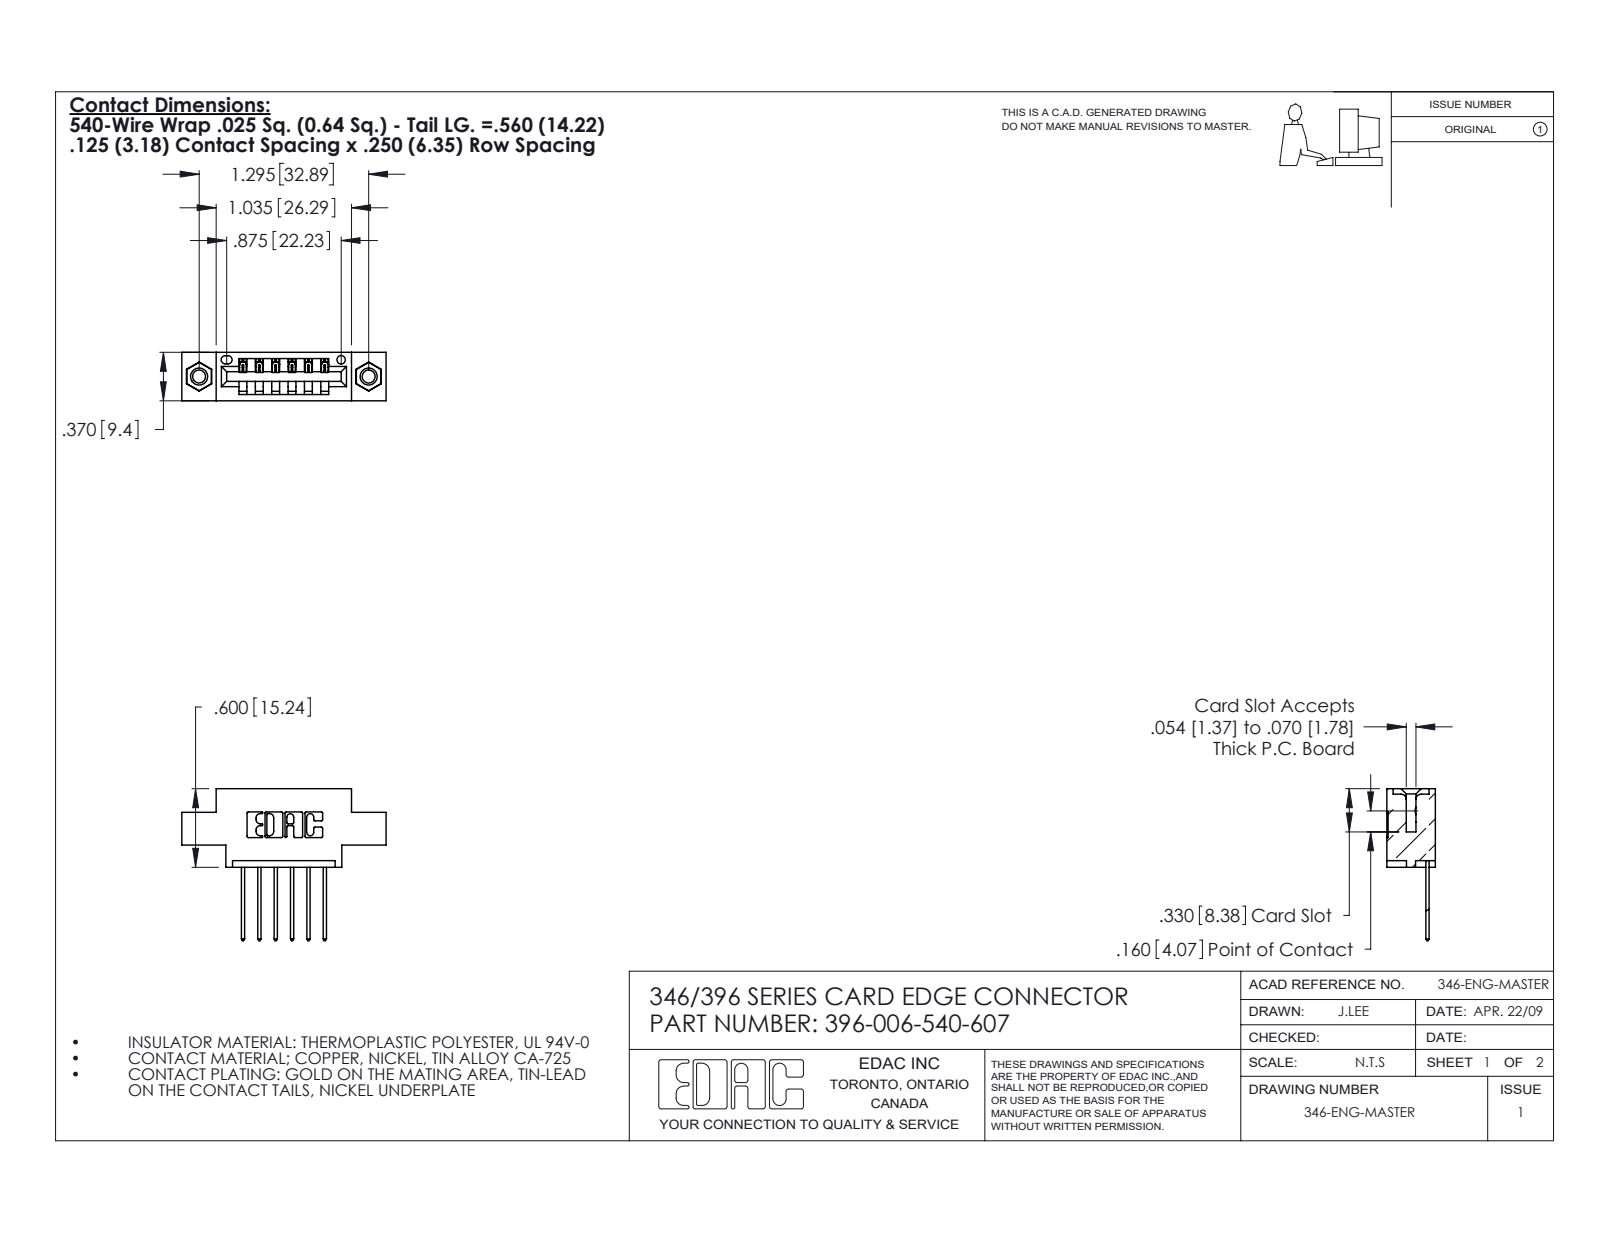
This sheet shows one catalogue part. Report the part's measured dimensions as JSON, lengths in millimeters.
{"part_name": "345-292-001_345-293-140; 346 Part_0.170 Offset - 0.156 Dia-TI; 345-250-001_345-250-005-103; 396-006-540-607", "step_written_by": "SolidWorks 2020 (CONFIG_CONTROL_DESIGN)", "units": "millimeters", "bodies": {"solids": 9, "faces": 534, "planar": 352, "cylindrical": 166, "other": 16}, "overall_size": [39.6, 29.5, 9.4], "volume_mm3": 3390, "surface_area_mm2": 4097, "round_holes": [[2.5, 2], [3.2, 2], [4, 2], [1.6, 1]], "round_bosses_or_shafts": [[3.9, 2]], "partial_cylinders_radius": [[0.3, 22], [0.2, 12], [0.3, 12], [0.2, 6], [0.8, 6], [0.7, 3], [0.8, 2], [1, 2]], "face_to_face_distances": [6.4, 9.4, 1.2, 8.2, 5.6, 3.8, 1.8, 7.6, 0.6, 2.5], "hole_center_spacings": [6.2, 27.7, 32.9]}
